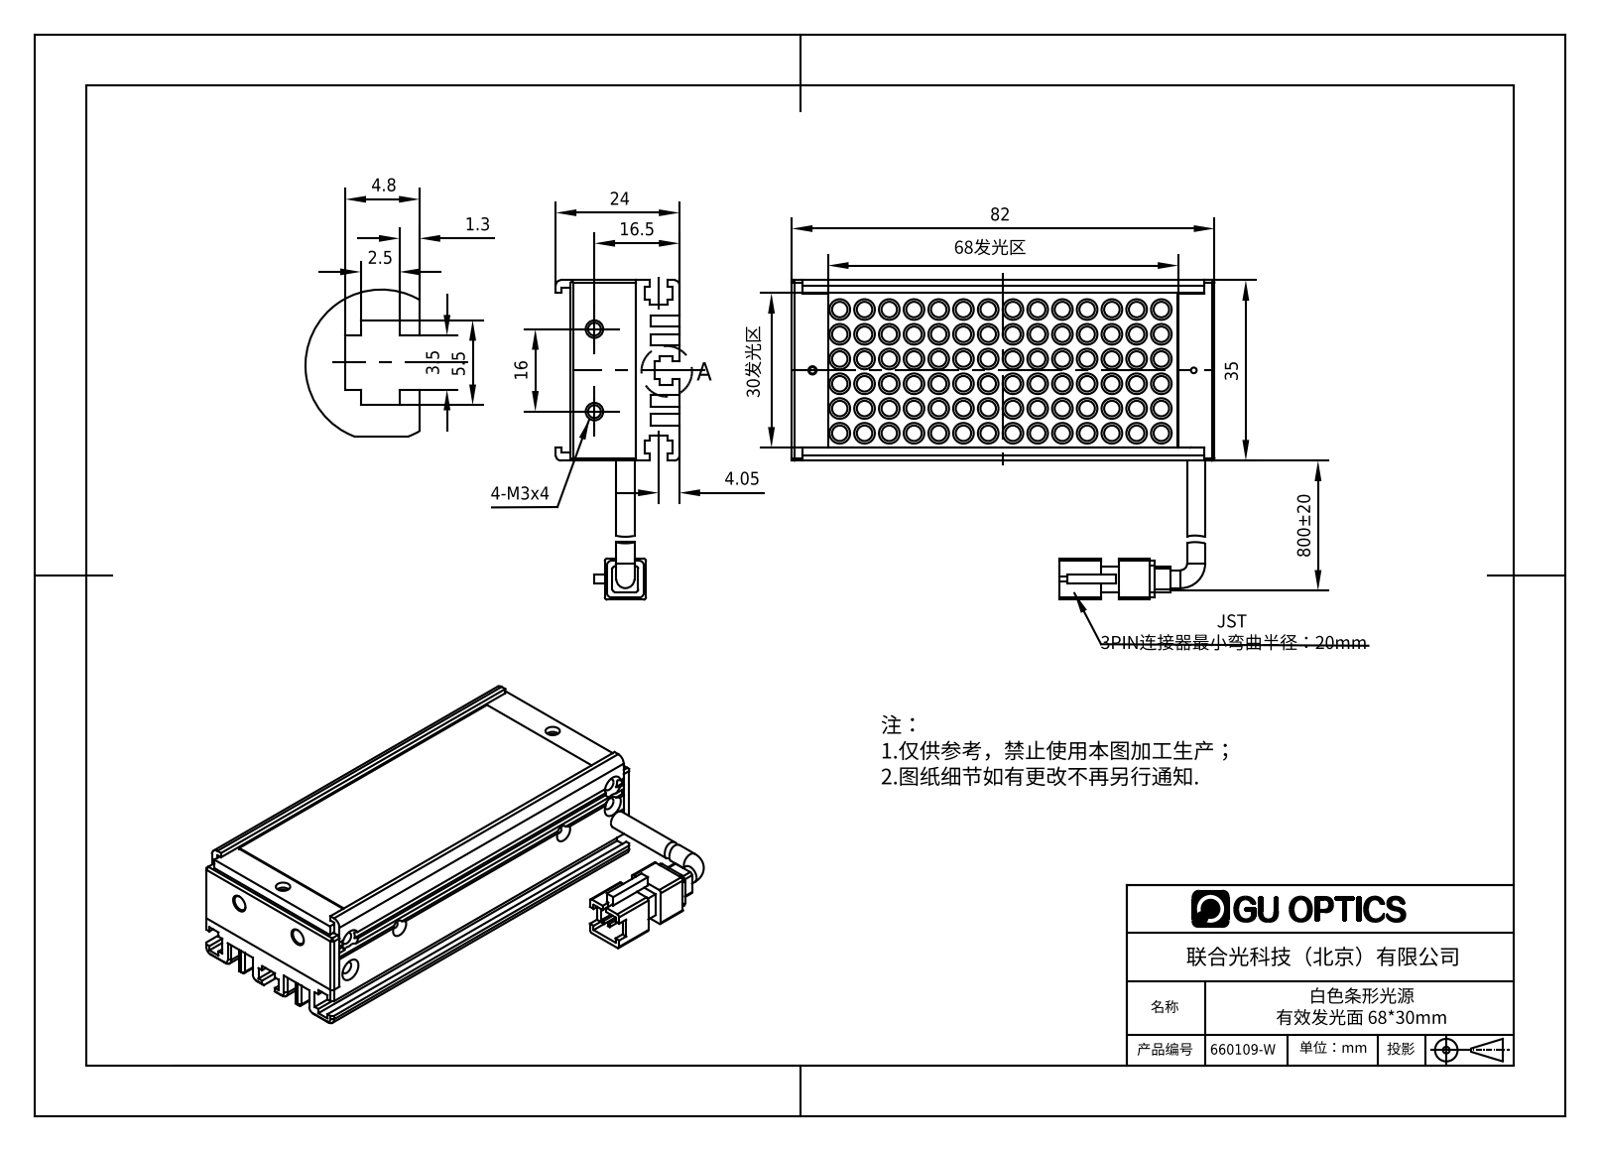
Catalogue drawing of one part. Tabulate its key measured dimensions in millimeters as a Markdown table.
| quantity | value |
| --- | --- |
| part name | 660109-W |
| STEP written by | SolidWorks 2016 (AUTOMOTIVE_DESIGN) |
| units | millimeters |
| bodies | 8 solids, 823 faces (326 planar, 272 cylindrical, 225 other) |
| overall size | 82 × 62 × 24 |
| volume | 37 515 mm³ |
| surface area | 41 983 mm² |
| round holes (diameter × count) | 1.6 × 5, 2.4 × 5, 1.25 × 4, 1.5 × 2, 2.5 × 2, 2.8 × 2, 3 × 2 |
| round bosses / shafts (diameter × count) | 3.1 × 84, 3.5 × 2 |
| partial cylindrical surfaces (radius × count) | 0.5 × 12, 1 × 8, 1.5 × 8, 1.65 × 2 |
| main face-to-face distances | 2, 2.2, 10.2, 8, 14, 12, 2.5, 10, 4, 8.6 |
| hole center spacings | 7, 72, 2.5, 4.5, 13.5, 13.79, 13.9, 14 |
